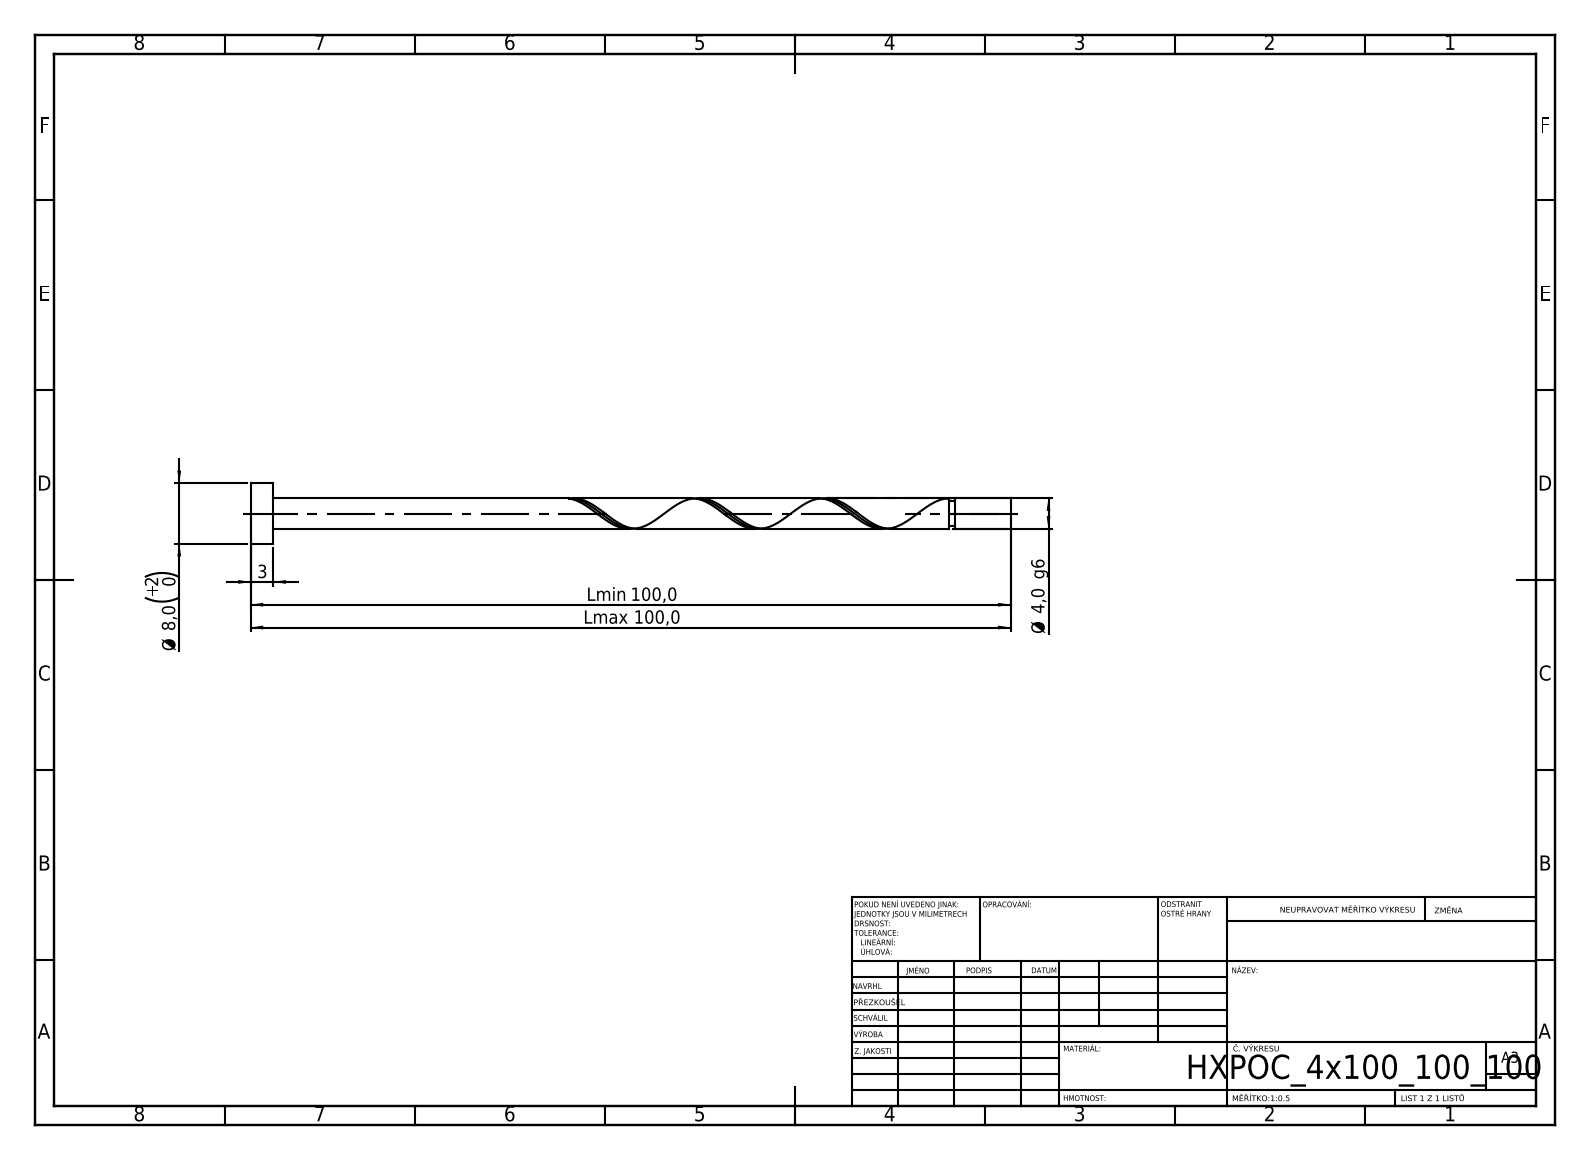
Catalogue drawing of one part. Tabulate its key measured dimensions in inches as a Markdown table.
| quantity | value |
| --- | --- |
| STEP written by | SolidWorks 2019 (CONFIG_CONTROL_DESIGN) |
| units | inches |
| bodies | 1 solid, 21 faces (6 planar, 14 cylindrical, 1 other) |
| overall size | 3.937 × 0.315 × 0.315 |
| volume | 0.083 in³ |
| surface area | 2.213 in² |
| round bosses / shafts (diameter × count) | 0.315 × 1, 0.157 × 1, 0.126 × 1 |
| main face-to-face distances | 0.118, 3.937, 3.819, 3.651, 3.533, 0.286, 3.62, 3.502, 0.031, 0.317 |
